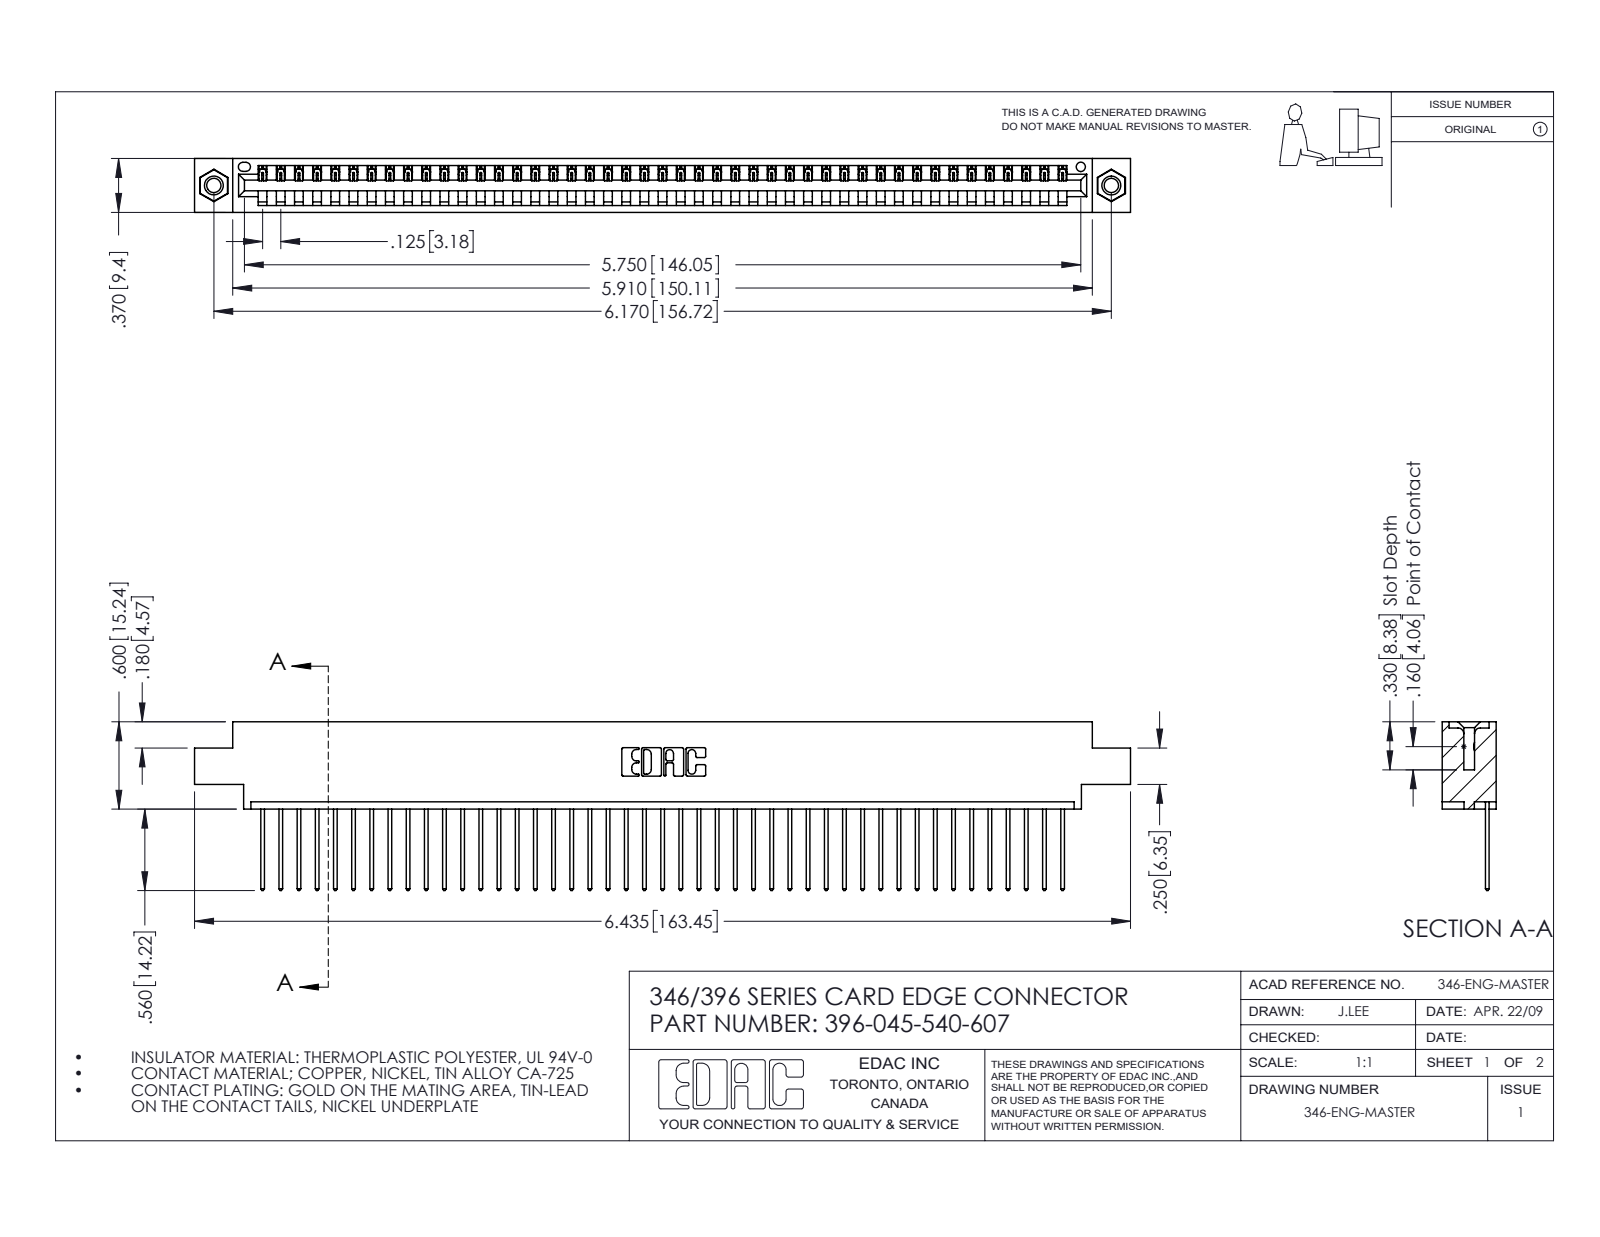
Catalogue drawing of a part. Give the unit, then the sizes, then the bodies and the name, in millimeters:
Units: millimetres
Overall size (bounding box): 163.4 × 29.5 × 9.4
Round holes (diameter × count): ⌀2.5 ×2, ⌀3.2 ×2, ⌀4 ×2, ⌀1.6 ×1
Round bosses / shafts (diameter × count): ⌀3.9 ×2
Partial cylindrical surfaces — rounded edges, fillets, slot ends (radius × count): R0.2 ×90, R0.3 ×90, R0.3 ×22, R0.2 ×6, R0.8 ×6, R0.7 ×3, R0.8 ×2, R1 ×2
Main face-to-face distances: 1.2, 8.2, 9.4, 6.4, 1.8, 7.6, 0.6, 5.6, 3.8, 2.5
Hole centre spacings: 6.2, 151.4, 156.7
Volume: 15 600 mm³ · Surface area: 20 120 mm²
Bodies: 48 solids, 2796 faces (1912 planar, 868 cylindrical, 16 other)
Part name (STEP PRODUCT): 345-292-001_345-293-140; 396-045-540-607; 345-250-001_345-250-005-103; 346 Part_0.170 Offset - 0.156 Dia-TI
STEP written by: SolidWorks 2016 (CONFIG_CONTROL_DESIGN)
